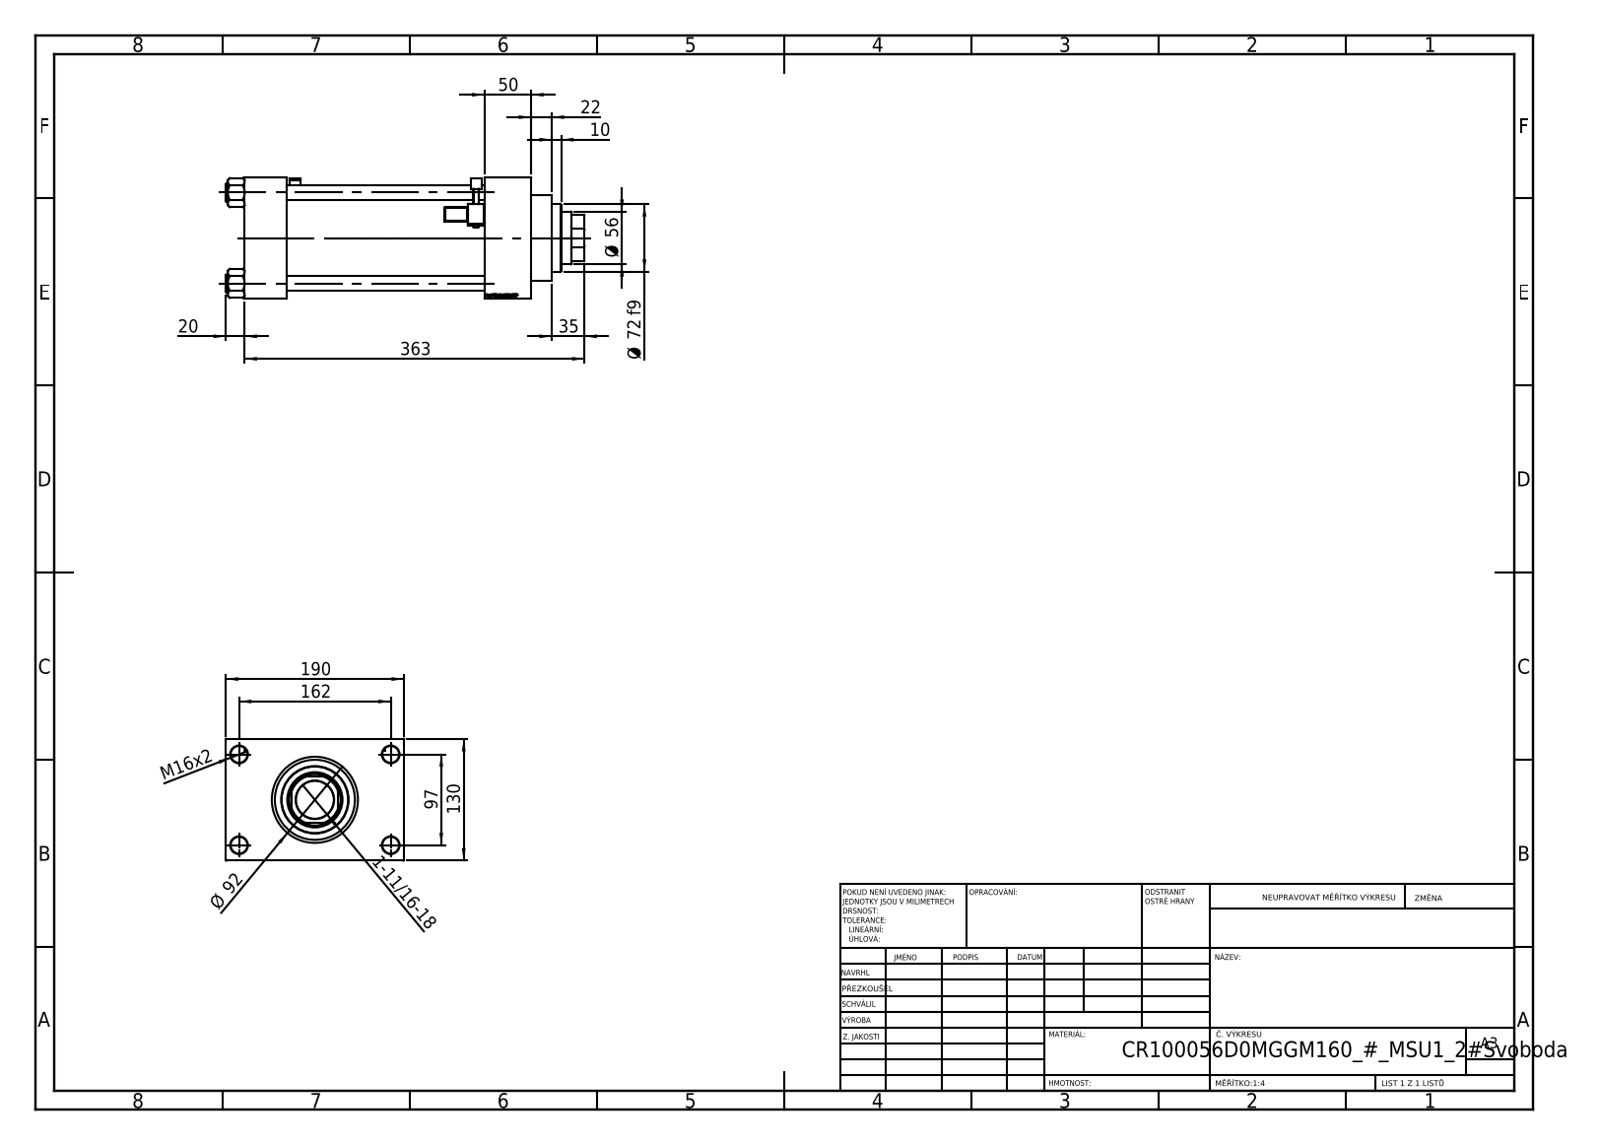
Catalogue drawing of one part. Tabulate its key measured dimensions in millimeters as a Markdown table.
| quantity | value |
| --- | --- |
| part name | NUT_M5_D; V215CR_D_Body; V215CR_VCP_D; V215CR_MSU (+2 more) |
| STEP written by | SolidWorks 2019 (CONFIG_CONTROL_DESIGN) |
| units | millimeters |
| bodies | 13 solids, 1306 faces (603 planar, 149 cylindrical, 554 other) |
| overall size | 383 × 190 × 130 |
| volume | 3 279 000 mm³ |
| surface area | 515 714 mm² |
| round holes (diameter × count) | 16 × 4, 18 × 4, 7 × 2, 26.44 × 2, 35 × 2, 40.5 × 1, 56 × 1, 59 × 1, 76 × 1, 85.5 × 1, 100 × 1 |
| round bosses / shafts (diameter × count) | 19 × 4, 6 × 2, 106 × 1, 92 × 1, 72 × 1 |
| partial cylindrical surfaces (radius × count) | 0.5 × 48, 1 × 2, 2.5 × 2, 4 × 2, 27 × 1 |
| main face-to-face distances | 130, 211, 50, 45, 256, 160, 306, 261, 30, 190 |
| hole center spacings | 32.55, 68.52, 94.41, 96.9, 102.27, 129.45, 161.73, 97 |
